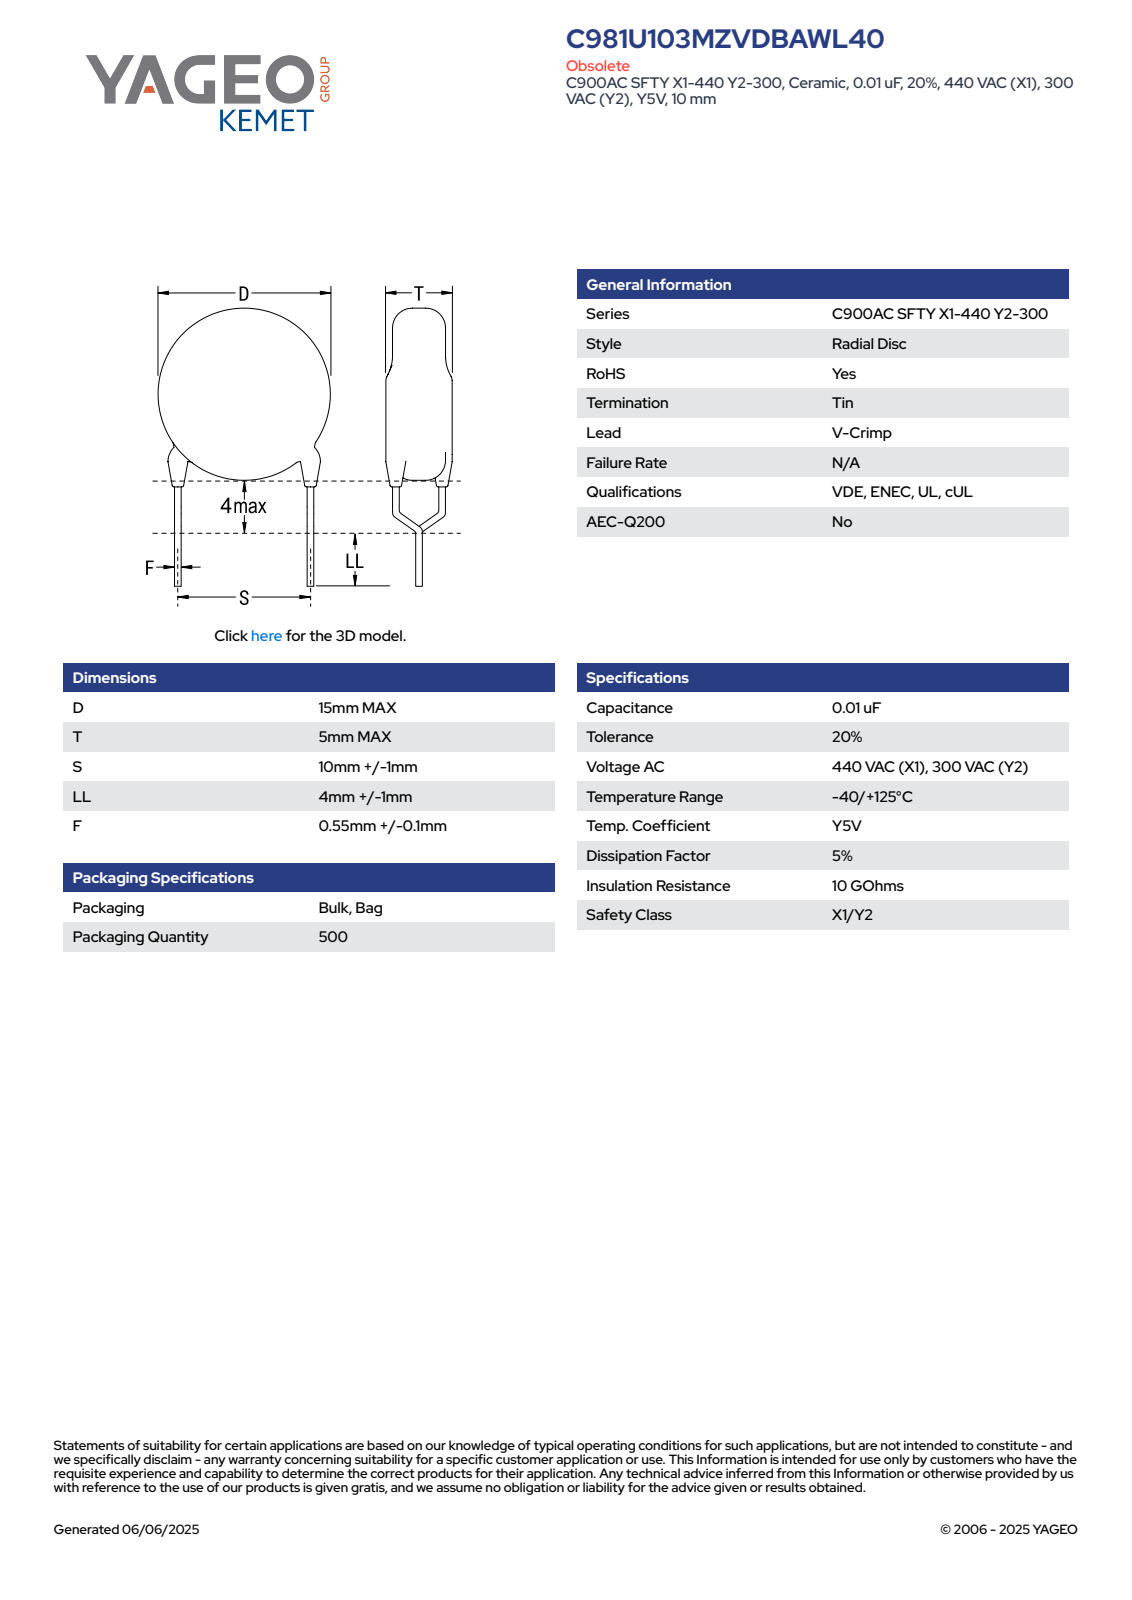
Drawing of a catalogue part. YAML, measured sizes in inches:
part_name: "CCD_VCC900_D15T5S10LL5F0.65"
step_written_by: "SolidWorks 2014 (AUTOMOTIVE_DESIGN)"
units: inches
bodies: {solids: 5, faces: 93, planar: 65, cylindrical: 16, other: 12}
overall_size: [0.937, 0.591, 0.197]
volume: 0.053
surface_area: 0.958
round_bosses_or_shafts:
  - {diameter: 0.026, count: 6}
  - {diameter: 0.591, count: 1}
face_to_face_distances: [0.197, 0.311, 0.68, 0.369, 0.603, 0.292, 0.077, 0.021, 0.313, 0.015]
